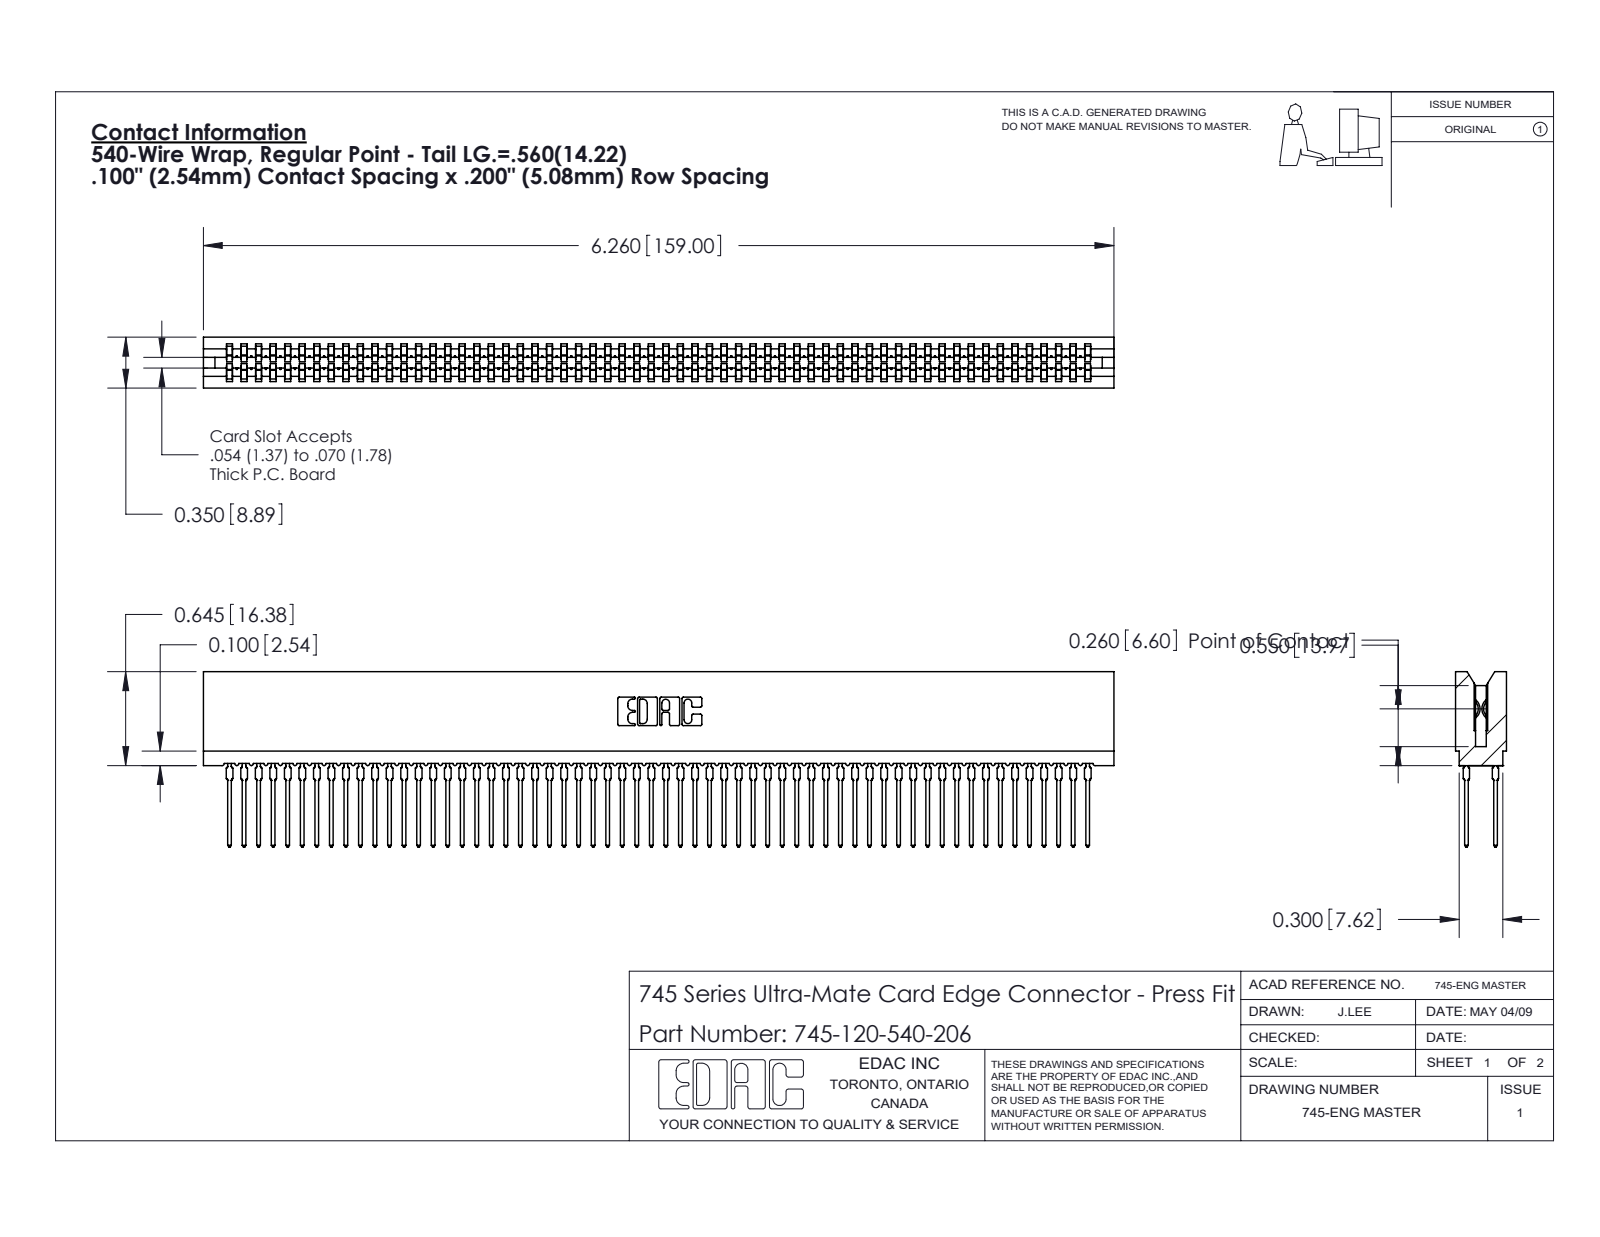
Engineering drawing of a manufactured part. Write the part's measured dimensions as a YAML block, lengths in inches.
part_name: "745-292-001_540; 745 Part_Insulator Option - 06; 745-120-540-206"
step_written_by: "SolidWorks 2020 (CONFIG_CONTROL_DESIGN)"
units: inches
bodies: {solids: 121, faces: 10836, planar: 5576, cylindrical: 2140, other: 3120}
overall_size: [6.26, 1.206, 0.35]
volume: 0.887
surface_area: 48.66
partial_cylinders:
  - {radius: 0.021, count: 240}
  - {radius: 0.015, count: 120}
  - {radius: 0.01, count: 22}
  - {radius: 0.005, count: 8}
  - {radius: 0.011, count: 8}
  - {radius: 0.007, count: 6}
  - {radius: 0.031, count: 6}
  - {radius: 0.026, count: 3}
face_to_face_distances: [0.063, 0.287, 0.35, 0.2, 0.045, 0.305, 0.018, 0.243, 0.138, 0.212]
